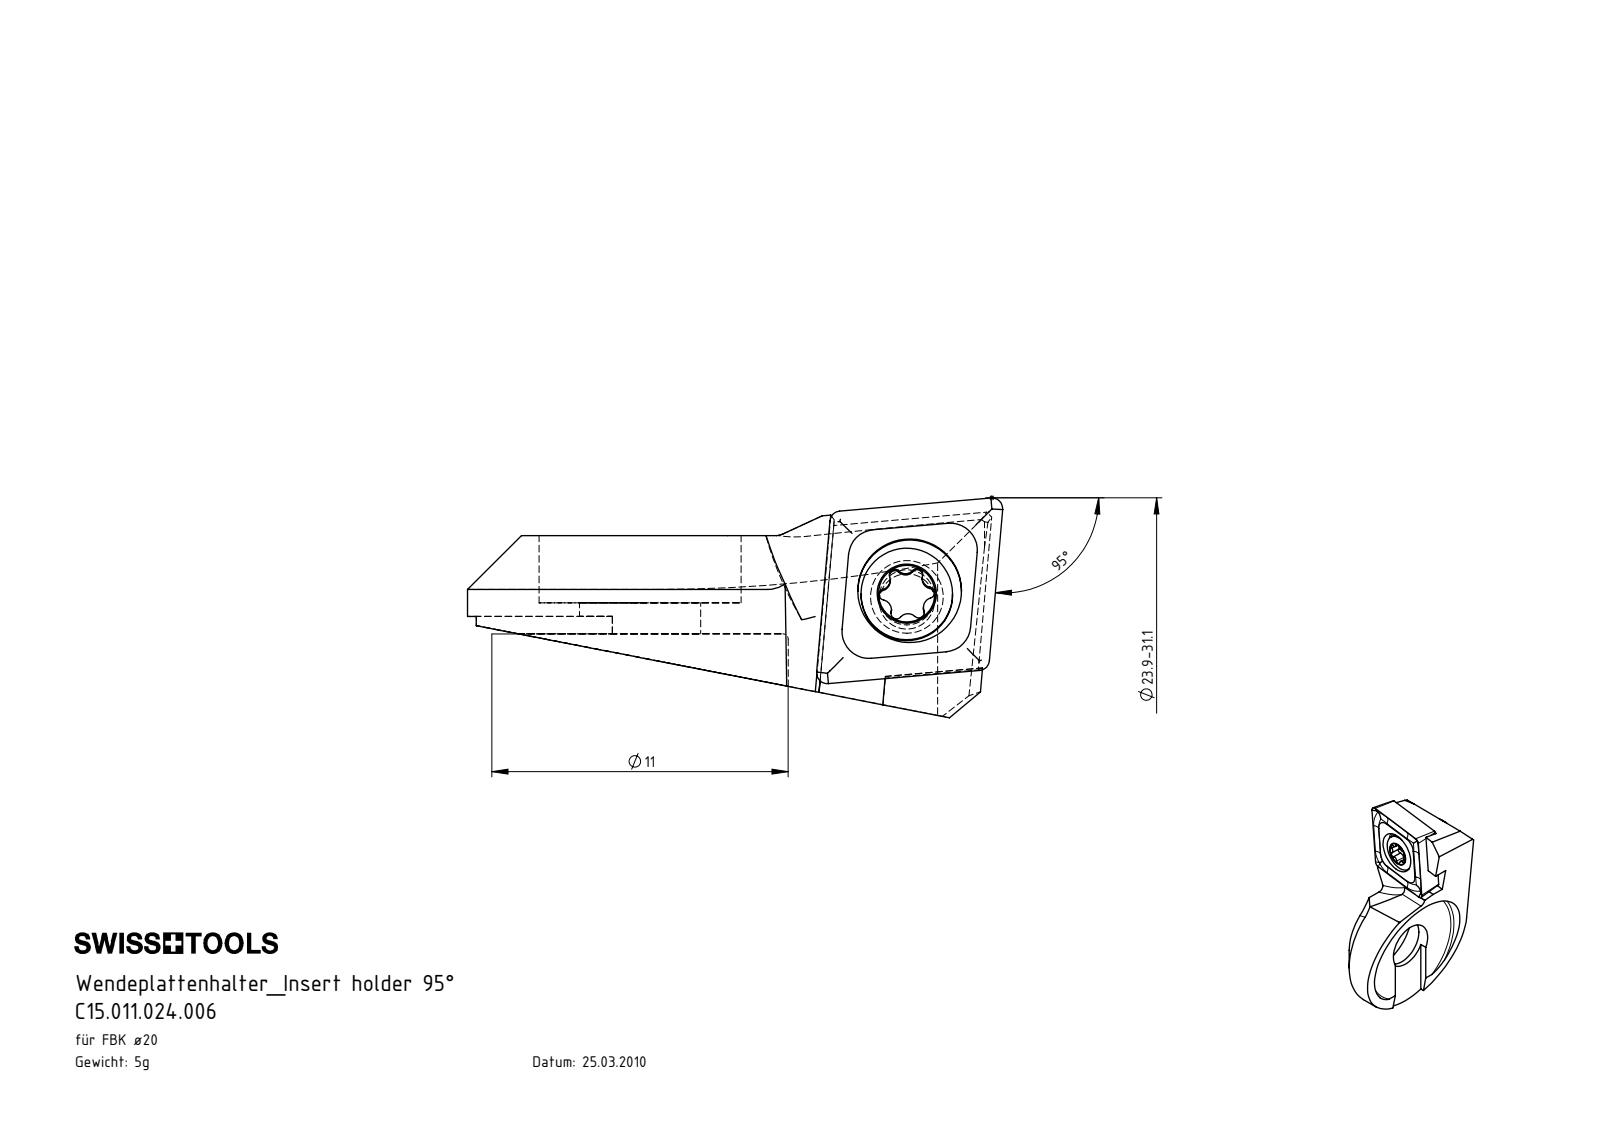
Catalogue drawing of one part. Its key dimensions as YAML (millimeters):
part_name: "C15.011.024.006; WCA-ER2.001.006_A; CCMT060204; F20-WCA.002.005_D_fertigbearbeitet"
step_written_by: "SolidWorks 2017 (CONFIG_CONTROL_DESIGN)"
units: millimeters
bodies: {solids: 3, faces: 131, planar: 40, cylindrical: 42, other: 49}
overall_size: [19.86, 12.8, 8.16]
volume: 549
surface_area: 847
round_holes:
  - {diameter: 2.05, count: 1}
  - {diameter: 2.8, count: 1}
  - {diameter: 3.85, count: 1}
  - {diameter: 4.5, count: 1}
  - {diameter: 7.5, count: 1}
round_bosses_or_shafts:
  - {diameter: 3.4, count: 1}
  - {diameter: 2.5, count: 1}
partial_cylinders:
  - {radius: 0.21, count: 6}
  - {radius: 0.36, count: 5}
  - {radius: 0.5, count: 2}
  - {radius: 5, count: 2}
  - {radius: 0.36, count: 1}
  - {radius: 5.5, count: 1}
  - {radius: 6.4, count: 1}
  - {radius: 10, count: 1}
face_to_face_distances: [1.15, 2.5, 3.65, 3, 0.5, 0.65, 2.38, 1.08, 1.3, 0.98]
